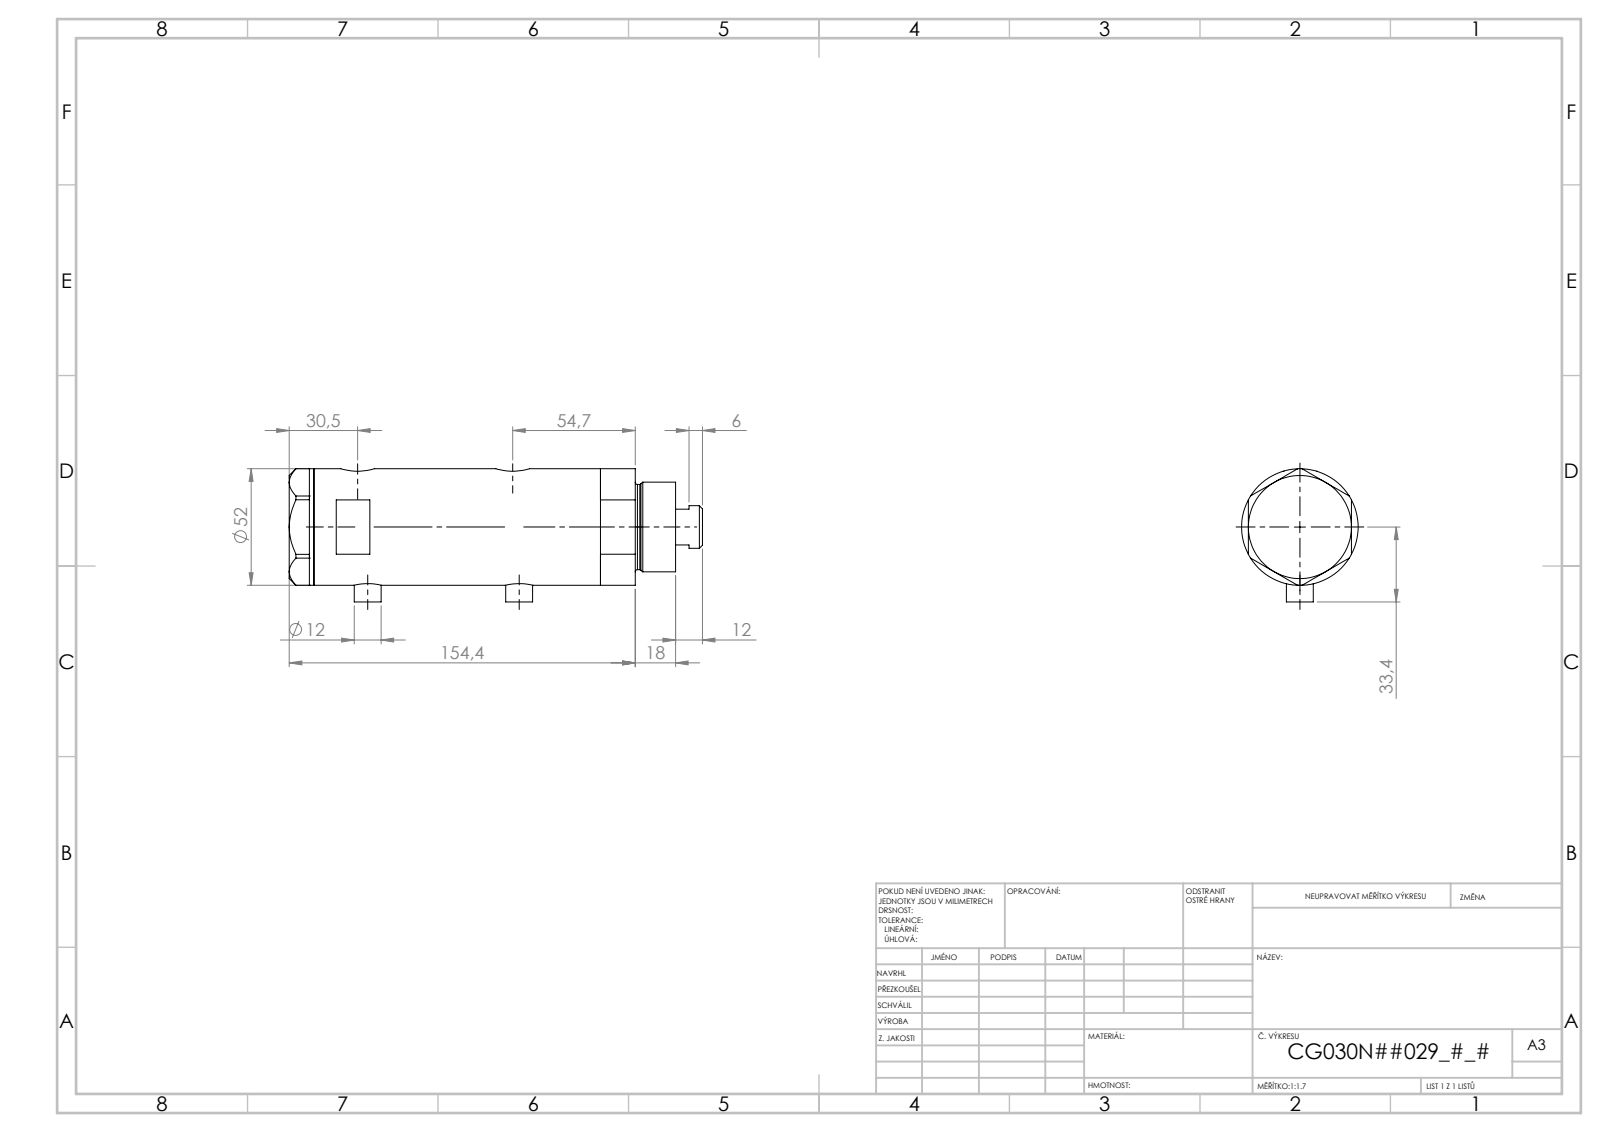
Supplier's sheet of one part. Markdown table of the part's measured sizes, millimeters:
| quantity | value |
| --- | --- |
| part name | V270CG_FRONT; V270CG_BACK; V270CG_MIDDLE; V270CG_VC |
| STEP written by | SolidWorks 2019 (CONFIG_CONTROL_DESIGN) |
| units | millimeters |
| bodies | 4 solids, 140 faces (67 planar, 53 cylindrical, 20 other) |
| overall size | 178.02 × 53.1 × 52 |
| volume | 317 718 mm³ |
| surface area | 74 382 mm² |
| round holes (diameter × count) | 5 × 2, 9.73 × 2, 12.5 × 2, 15 × 2, 6.5 × 1, 20 × 1, 21.5 × 1, 30 × 1, 33 × 1, 44 × 1 |
| round bosses / shafts (diameter × count) | 12 × 2, 52 × 1, 40 × 1, 38 × 1, 19 × 1 |
| main face-to-face distances | 23.81, 10.99, 34.8, 46, 93.55, 82.56, 58.75, 129.95, 118.96, 95.15 |
| hole center spacings | 2.9, 4.5, 55.75, 58.65, 60.25, 63.15, 2.89, 2.91 |
